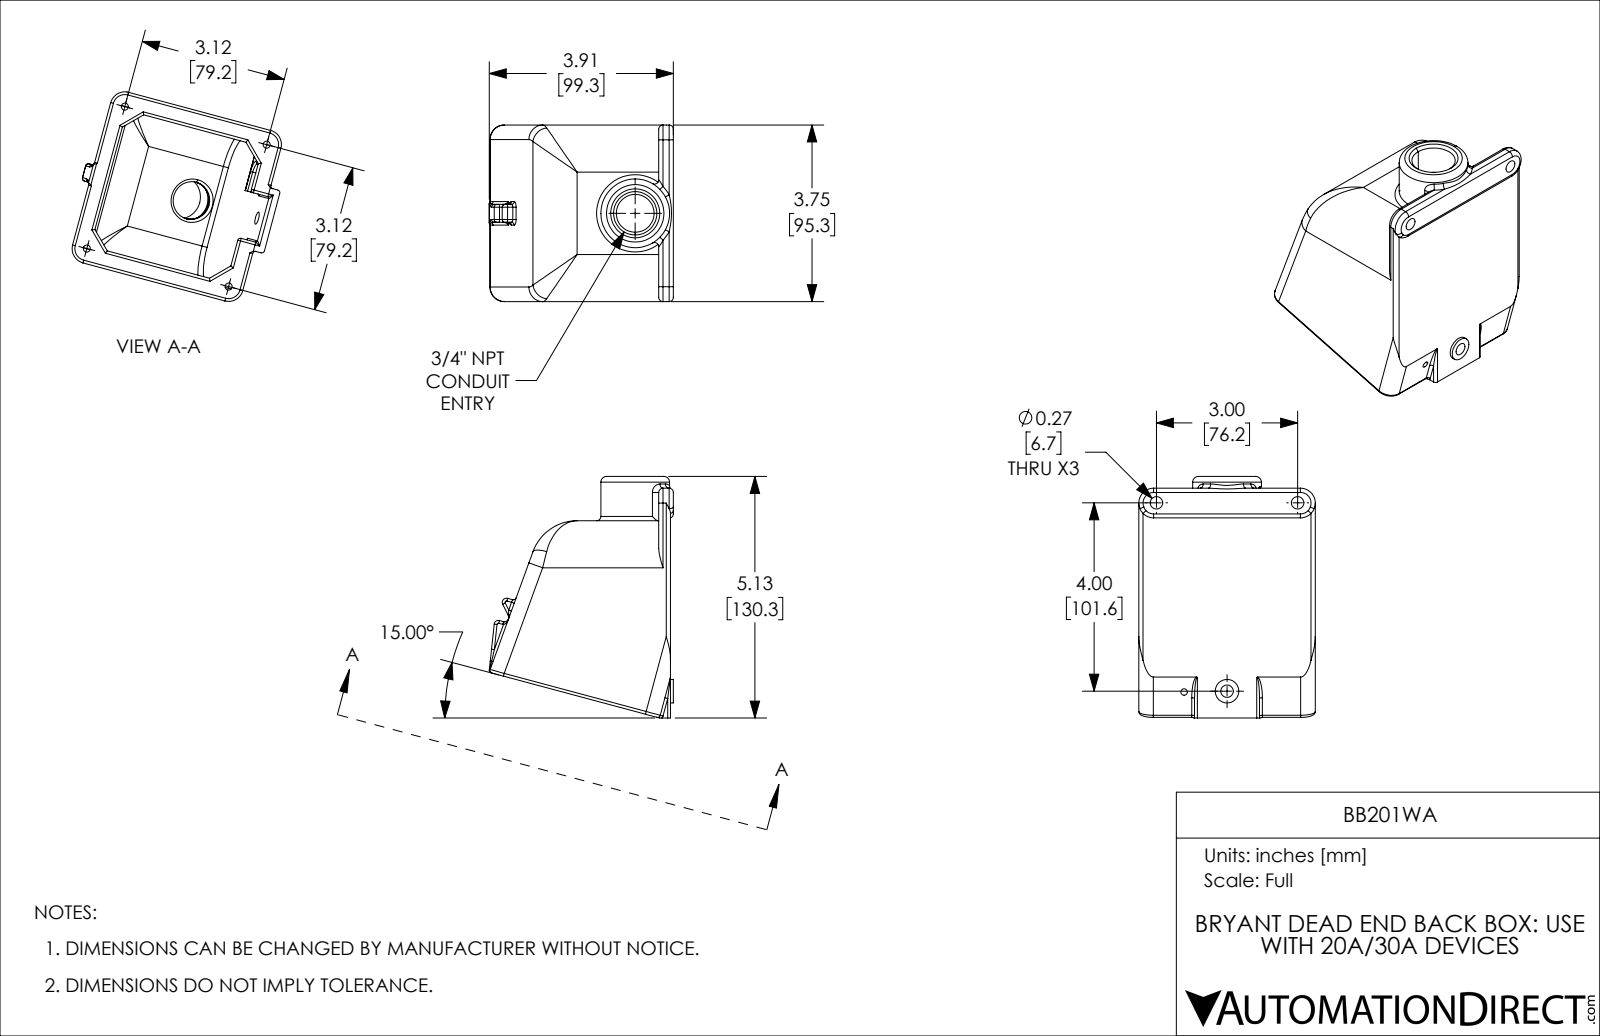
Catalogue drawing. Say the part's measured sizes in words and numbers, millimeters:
The part is named "BB201WA". Its 3-D file was written by "SolidWorks 2021 (CONFIG_CONTROL_DESIGN)". It is 1 solid with 428 faces: 63 planar, 244 cylindrical and 121 other. Overall it measures 130.3 by 99.4 by 95.3 millimeters. Its volume is 208 000 cubic millimeters and its surface area 82 770 square millimeters. Round holes: 4 of diameter 3.8, 2 of diameter 6.7, 1 of diameter 3.5, 1 of diameter 6.7, 1 of diameter 20.4, 1 of diameter 23.4, 1 of diameter 28.4. Round bosses or shafts: 1 of diameter 37.1, 1 of diameter 12.7. Partial cylindrical surfaces (rounded edges, fillets, slot ends): 59 of radius 1.5, 21 of radius 2.3, 4 of radius 3, 4 of radius 6.4, 4 of radius 7.9, 3 of radius 20.6, 3 of radius 25.4, 2 of radius 0.9. The main face-to-face distances are 4.8, 90.4, 85.6, 95.3, 6.4, 1.5, 0.8, 89.7, 94.5, 4.1. The hole center spacings are 79.2, 79.2, 108.5, 112.1, 23.2, 76.2, 103.1, 119.
